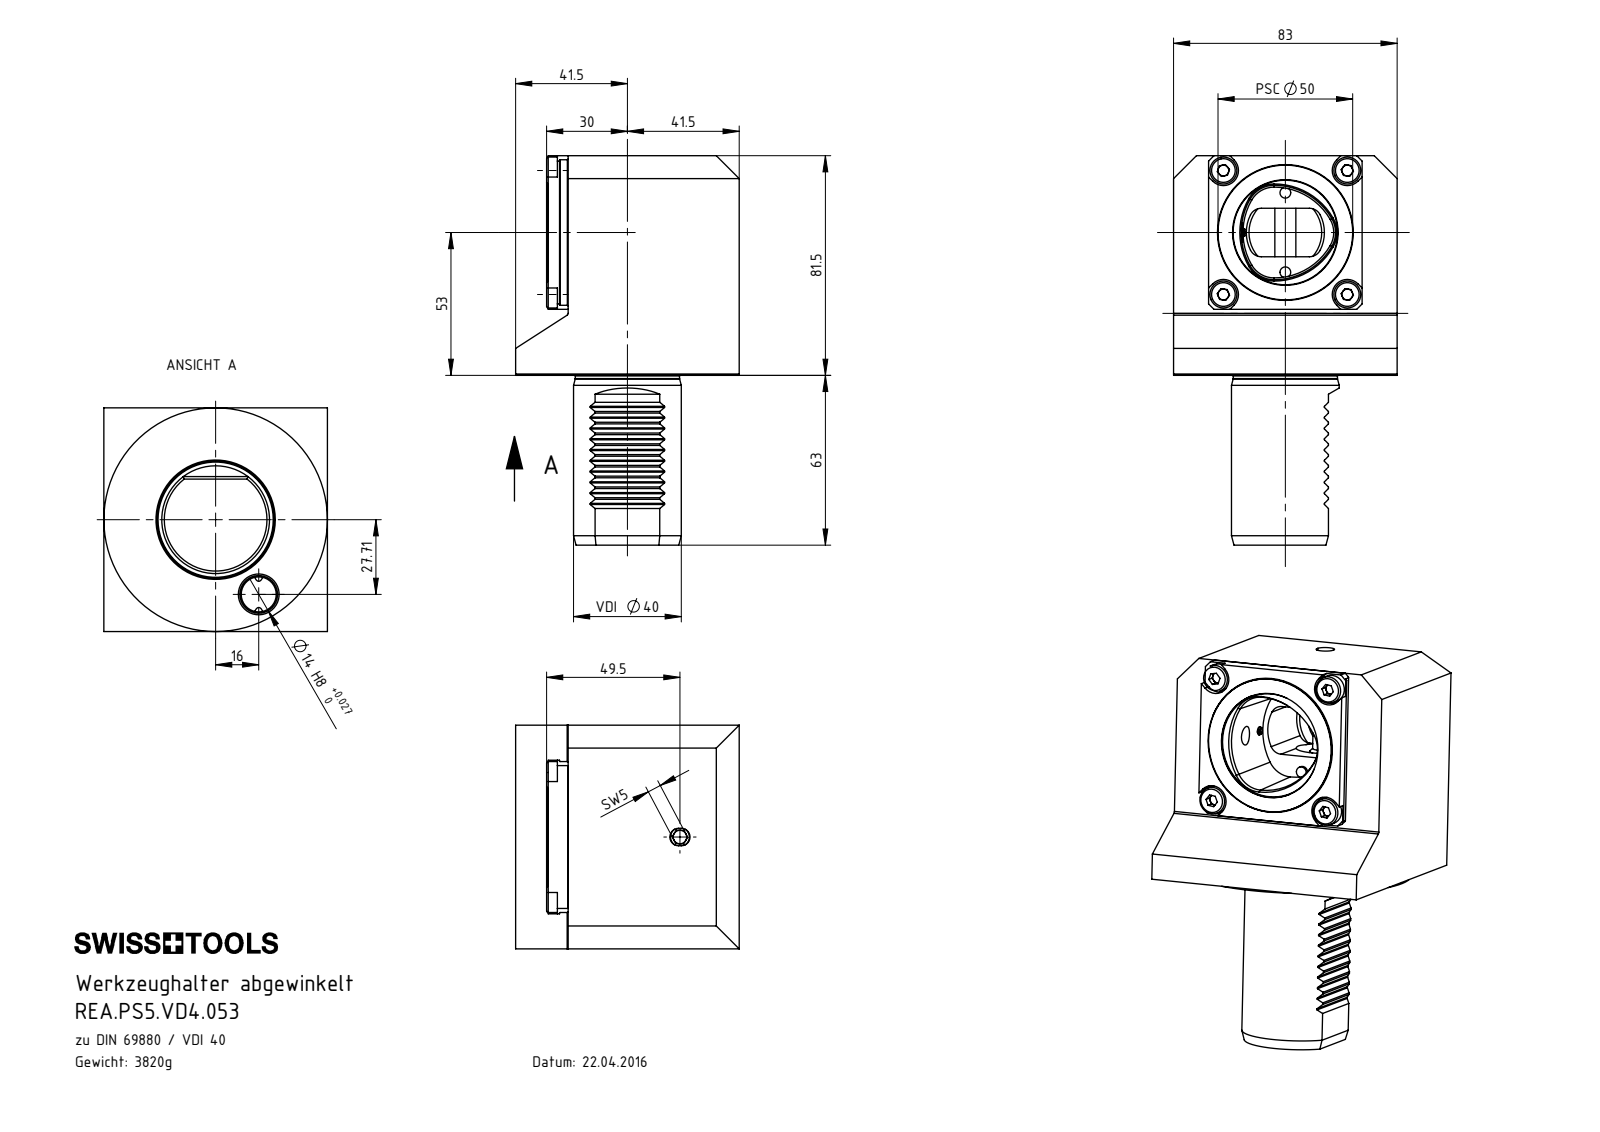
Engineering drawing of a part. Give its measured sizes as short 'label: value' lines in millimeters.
name: REA-PS5.VD4.053_A; U50-PS5.ER1.030_A; REA.PS5.VD4.053; ISO 8752 3x10 (+8 more)
written by: SolidWorks 2017 (AUTOMOTIVE_DESIGN)
unit: mm
bodies: 19 solids, 541 faces (283 planar, 108 cylindrical, 150 other)
size: 144.5 × 83 × 83
volume: 490 981 mm³; area: 91 222 mm²
holes: 6× ⌀5, 4× ⌀6.2, 3× ⌀4, 3× ⌀4.2, 2× ⌀3.3, 1× ⌀2.1, 1× ⌀3, 1× ⌀7, 1× ⌀9, 1× ⌀13, 1× ⌀14, 1× ⌀27
bosses: 5× ⌀10, 4× ⌀6, 2× ⌀7, 2× ⌀4, 1× ⌀83, 1× ⌀50, 1× ⌀49.7, 1× ⌀46.8
rounds: 10× R0.3, 6× R0.1, 4× R4.5, 4× R5.6, 2× R0.2, 2× R3.25, 2× R4, 1× R0.8
face distances: 83, 63.5, 81.5, 13.5, 50, 0.5, 81, 27, 8, 19.5
hole spacings: 24.43, 32.53, 44.2, 46, 14.75, 15.01, 19.55, 20.5
